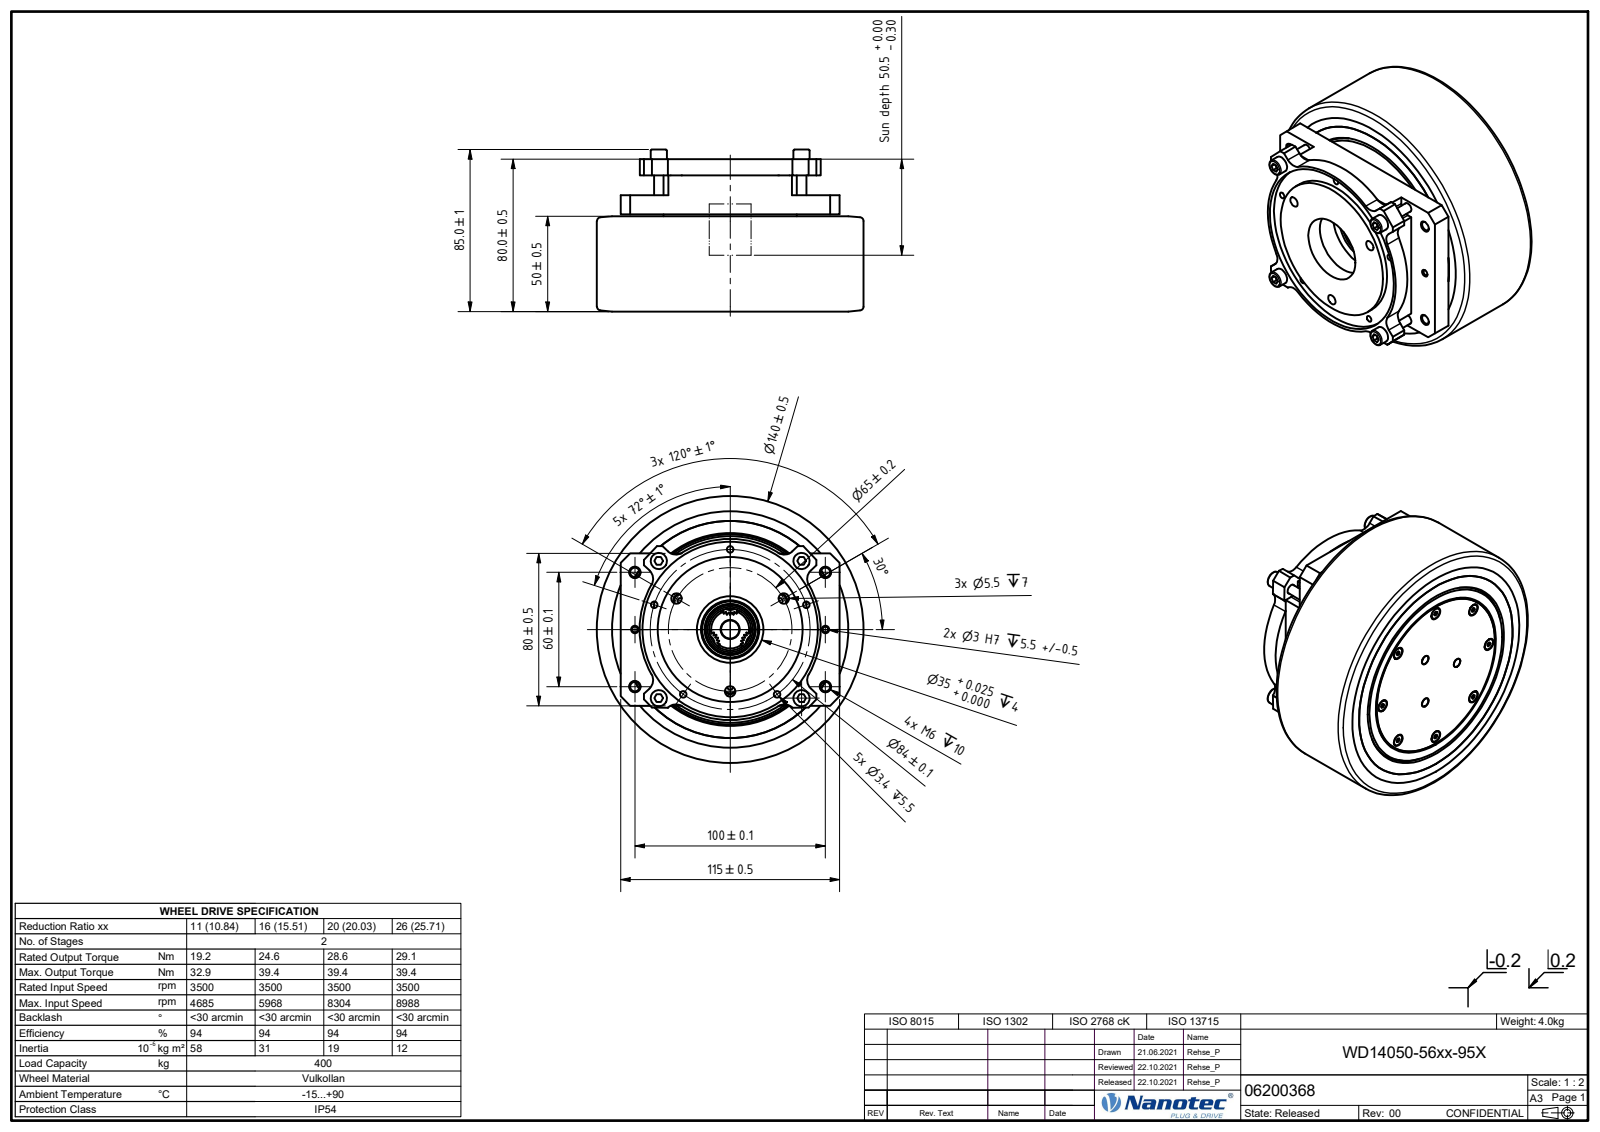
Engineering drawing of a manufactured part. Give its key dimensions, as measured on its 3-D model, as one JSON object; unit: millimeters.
{"part_name": "D-00004081_Shrinkwrap_1", "step_written_by": "Autodesk Inventor 2019 (AUTOMOTIVE_DESIGN)", "units": "millimeters", "bodies": {"solids": 1, "faces": 301, "planar": 171, "cylindrical": 67, "other": 63}, "overall_size": [140, 140, 85], "volume_mm3": 976219, "surface_area_mm2": 83179, "round_holes": [[5.5, 7], [3.4, 5], [4.13, 4], [4.92, 4], [4.97, 3], [3, 2], [35, 1], [40, 1], [92, 1]], "round_bosses_or_shafts": [[6, 8], [5, 7], [8.5, 4], [140, 1], [88, 1], [76, 1], [74, 1]], "partial_cylinders_radius": [[6, 8], [5, 4], [47.5, 1]], "face_to_face_distances": [50, 80, 1, 51, 30, 29, 20.5, 61, 11, 10], "hole_center_spacings": [28.15, 42, 13.87, 30, 38.11, 49.37, 51.98, 58.31]}
